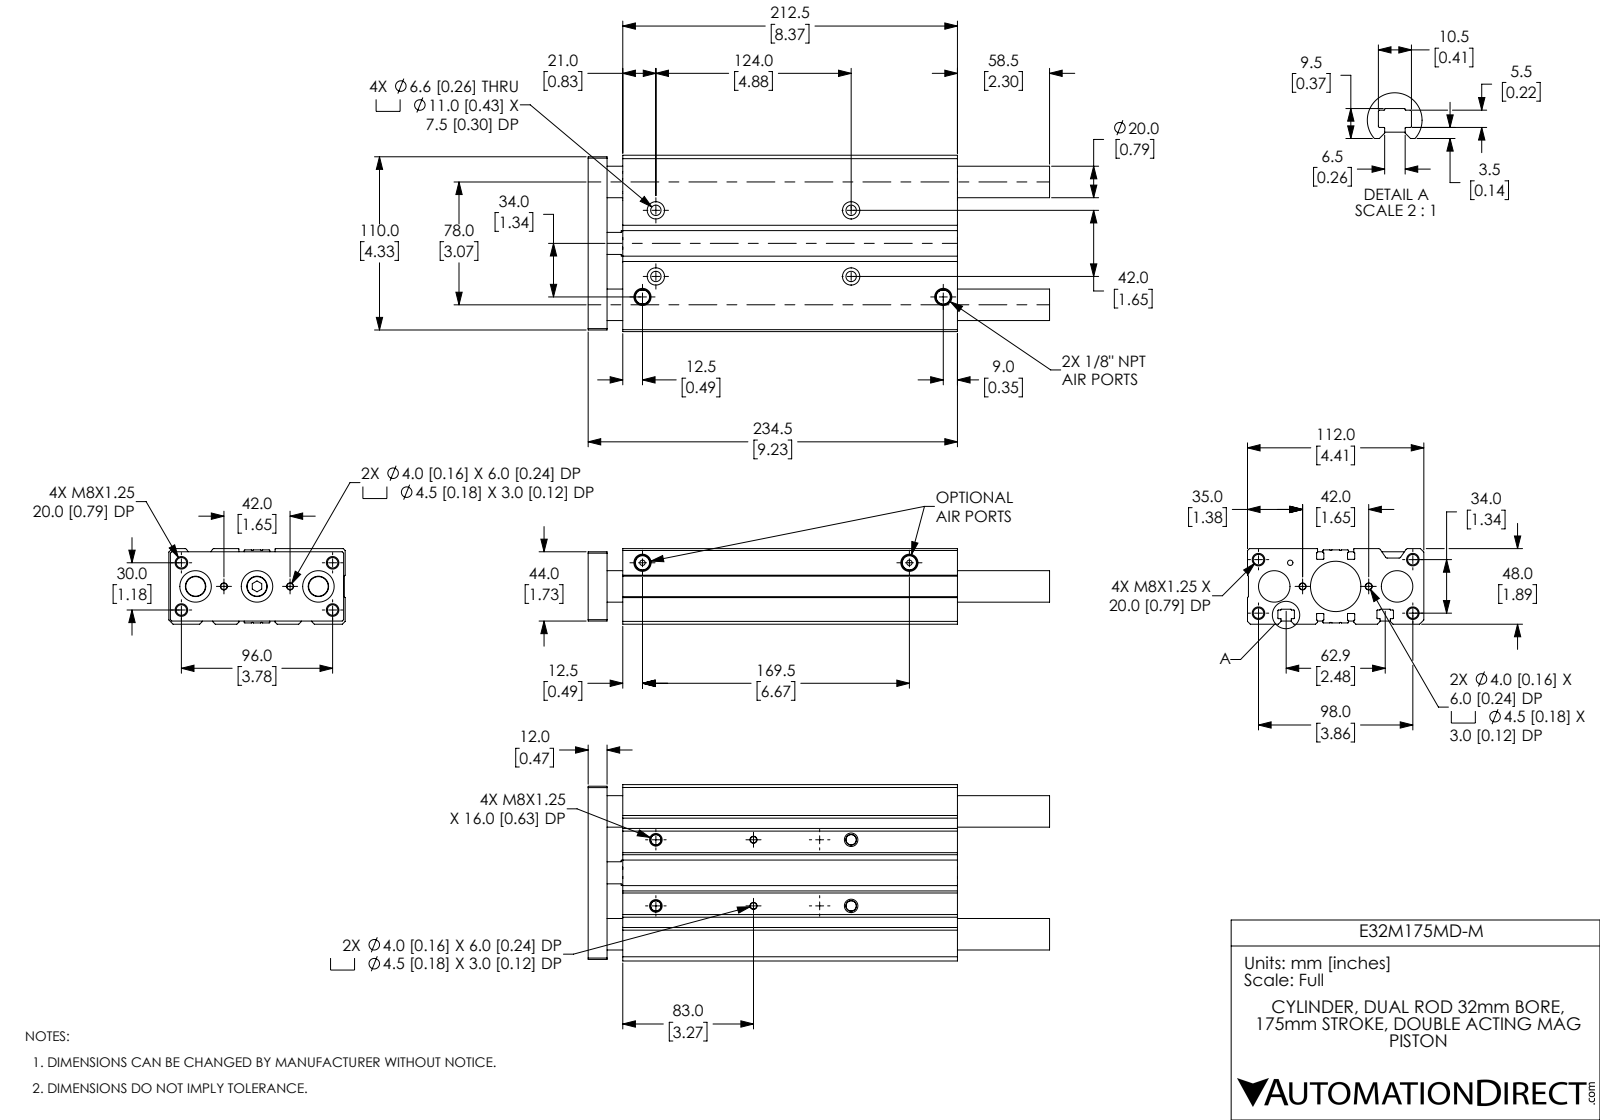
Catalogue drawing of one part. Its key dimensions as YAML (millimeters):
part_name: "E32M175MD-M_BODY; E32M175MD-M_ENDPLATE; E32M175MD-M"
step_written_by: "SolidWorks 2019 (CONFIG_CONTROL_DESIGN)"
units: millimeters
bodies: {solids: 5, faces: 423, planar: 139, cylindrical: 190, other: 94}
overall_size: [293, 112, 48]
volume: 1032000
surface_area: 223316
round_holes:
  - {diameter: 6.65, count: 12}
  - {diameter: 4, count: 4}
  - {diameter: 4.5, count: 4}
  - {diameter: 6.6, count: 4}
  - {diameter: 11, count: 4}
  - {diameter: 10, count: 3}
  - {diameter: 20, count: 3}
  - {diameter: 3.43, count: 2}
  - {diameter: 12.95, count: 2}
  - {diameter: 3.43, count: 1}
  - {diameter: 20, count: 1}
  - {diameter: 32, count: 1}
round_bosses_or_shafts:
  - {diameter: 16, count: 1}
  - {diameter: 12.95, count: 1}
partial_cylinders:
  - {radius: 0.2, count: 32}
  - {radius: 0.4, count: 28}
  - {radius: 1.2, count: 4}
  - {radius: 0.3, count: 2}
face_to_face_distances: [48, 6, 0.8, 112, 47.2, 37.7, 41.2, 0.6, 38.5, 22]
hole_center_spacings: [2.24, 17.49, 19.72, 30.89, 32.02, 32.76, 42, 50.29]
